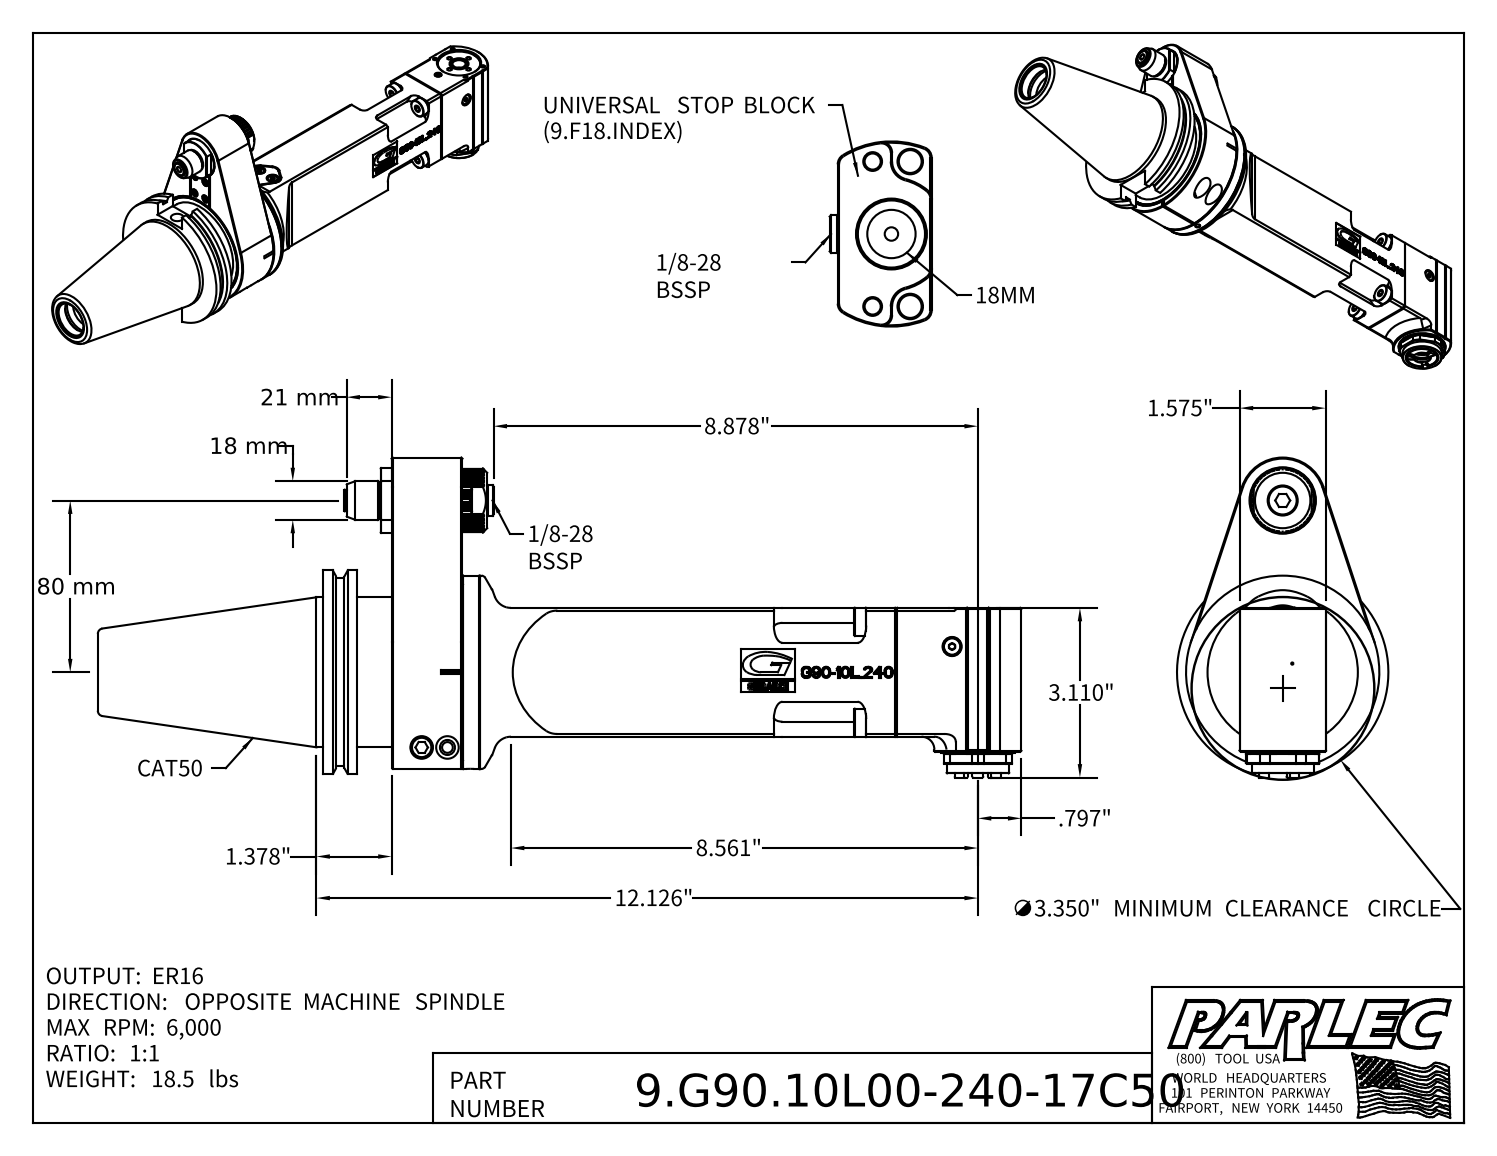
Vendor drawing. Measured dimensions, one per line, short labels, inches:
name: 9.G90.10L00-240-17C50; 9_GA1_458_1 (Classic, Type 1, Cat50, 80mm); 9_G90_10L240
written by: Autodesk Inventor 2022 (AUTOMOTIVE_DESIGN)
unit: in
bodies: 4 solids, 1550 faces (970 planar, 263 cylindrical, 317 other)
size: 16.931 × 5.866 × 3.875
volume: 64.15 in³; area: 351.8 in²
holes: 10× ⌀0.165, 6× ⌀0.335, 5× ⌀0.236, 4× ⌀0.098, 4× ⌀0.118, 3× ⌀0.157, 3× ⌀0.197, 3× ⌀0.413, 2× ⌀0.276, 2× ⌀1.26, 2× ⌀1.378, 1× ⌀0.13
bosses: 4× ⌀0.512, 3× ⌀0.394, 2× ⌀0.669, 2× ⌀0.307, 1× ⌀3.875, 1× ⌀3.593, 1× ⌀3.543, 1× ⌀3.228
rounds: 8× R0.157, 4× R0.236, 4× R0.315, 4× R1.106, 3× R0.079, 2× R0.059, 2× R0.085, 2× R0.197
face distances: 1.575, 1.299, 2.362, 0.626, 0.315, 1.252, 1.567, 1.925, 2.551, 1.378
hole spacings: 1.476, 2.557, 0.394, 0.435, 0.557, 0.728, 0.764, 1.087
